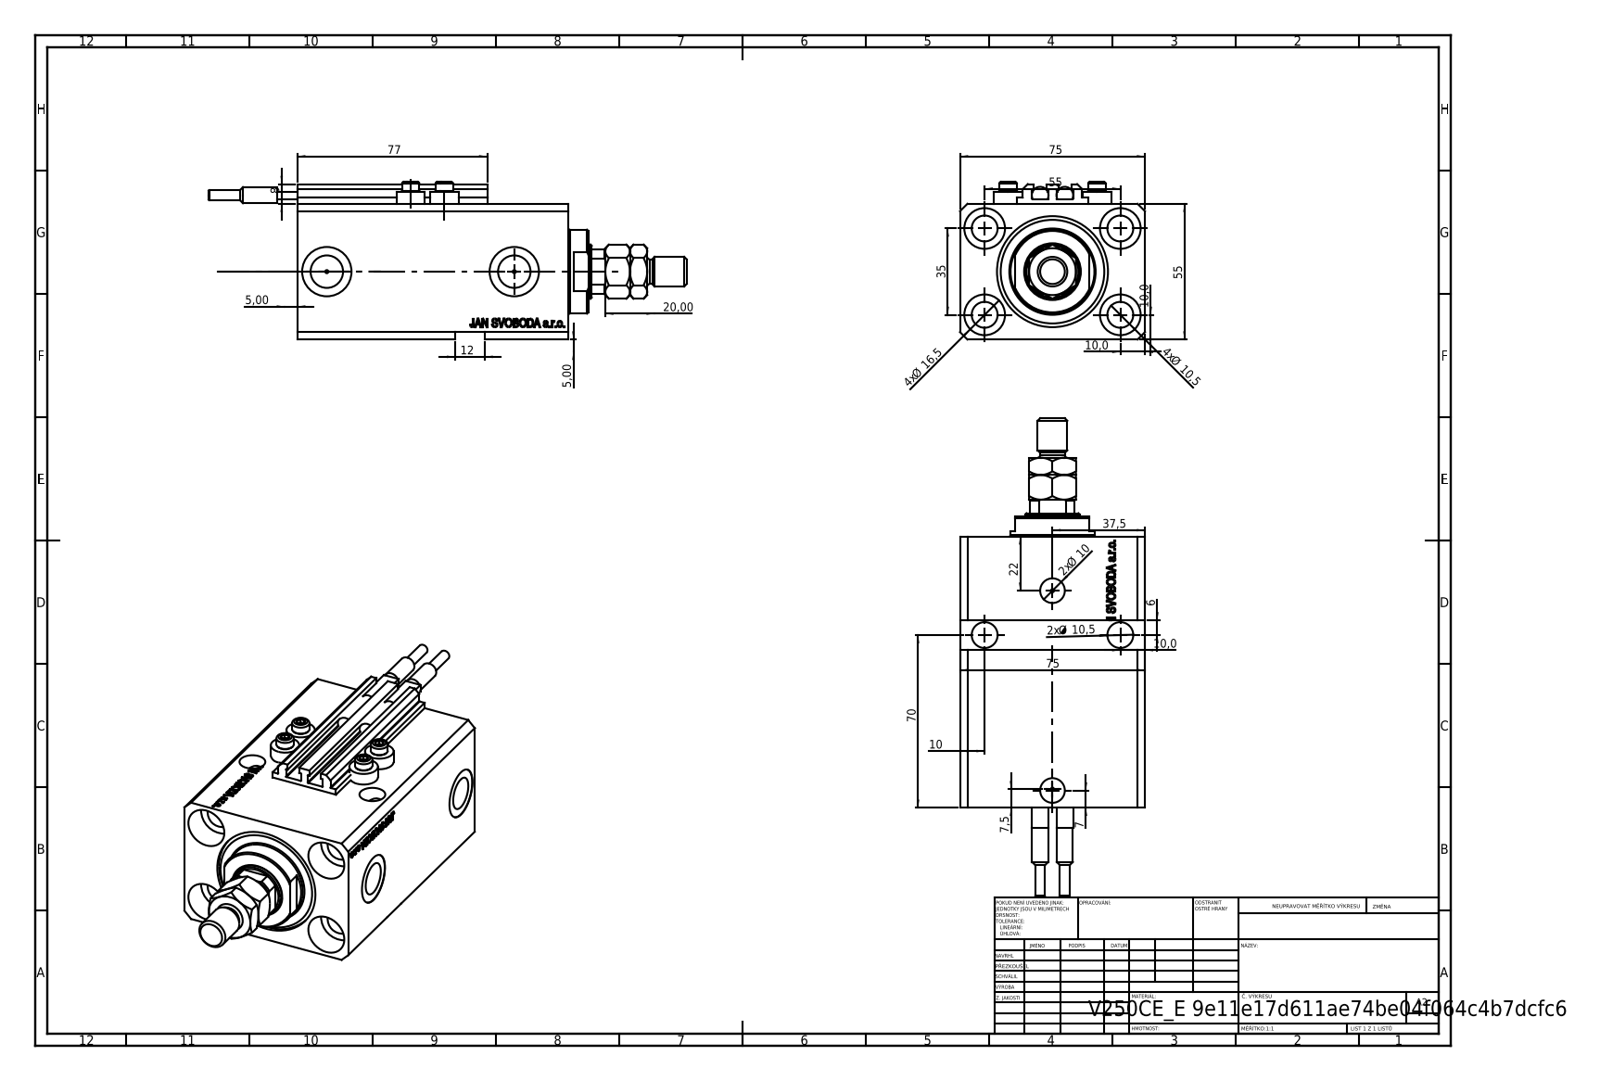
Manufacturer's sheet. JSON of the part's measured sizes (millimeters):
{"part_name": "V250CE_VC_E; MTA; V250CE_E_Body; V250CE_C_VCP (+2 more)", "step_written_by": "SolidWorks 2019 (CONFIG_CONTROL_DESIGN)", "units": "millimeters", "bodies": {"solids": 11, "faces": 1181, "planar": 565, "cylindrical": 154, "other": 462}, "overall_size": [193.9, 75, 64], "volume_mm3": 394690, "surface_area_mm2": 102918, "round_holes": [[10.5, 7], [1.25, 4], [4, 4], [16.5, 4], [10, 2], [13.16, 2], [20, 2], [22, 1], [32, 1], [45, 1]], "round_bosses_or_shafts": [[11.6, 4], [7, 4], [6.8, 2], [6.5, 2], [4, 2], [34, 1], [12, 1], [10, 1]], "partial_cylinders_radius": [[0.2, 10], [10.5, 1]], "face_to_face_distances": [55, 75, 3, 110, 57, 82.9, 27.1, 9.9, 73, 100.1], "hole_center_spacings": [32.6, 55, 13.6, 14.09, 25.81, 32.87, 33.62, 35]}
